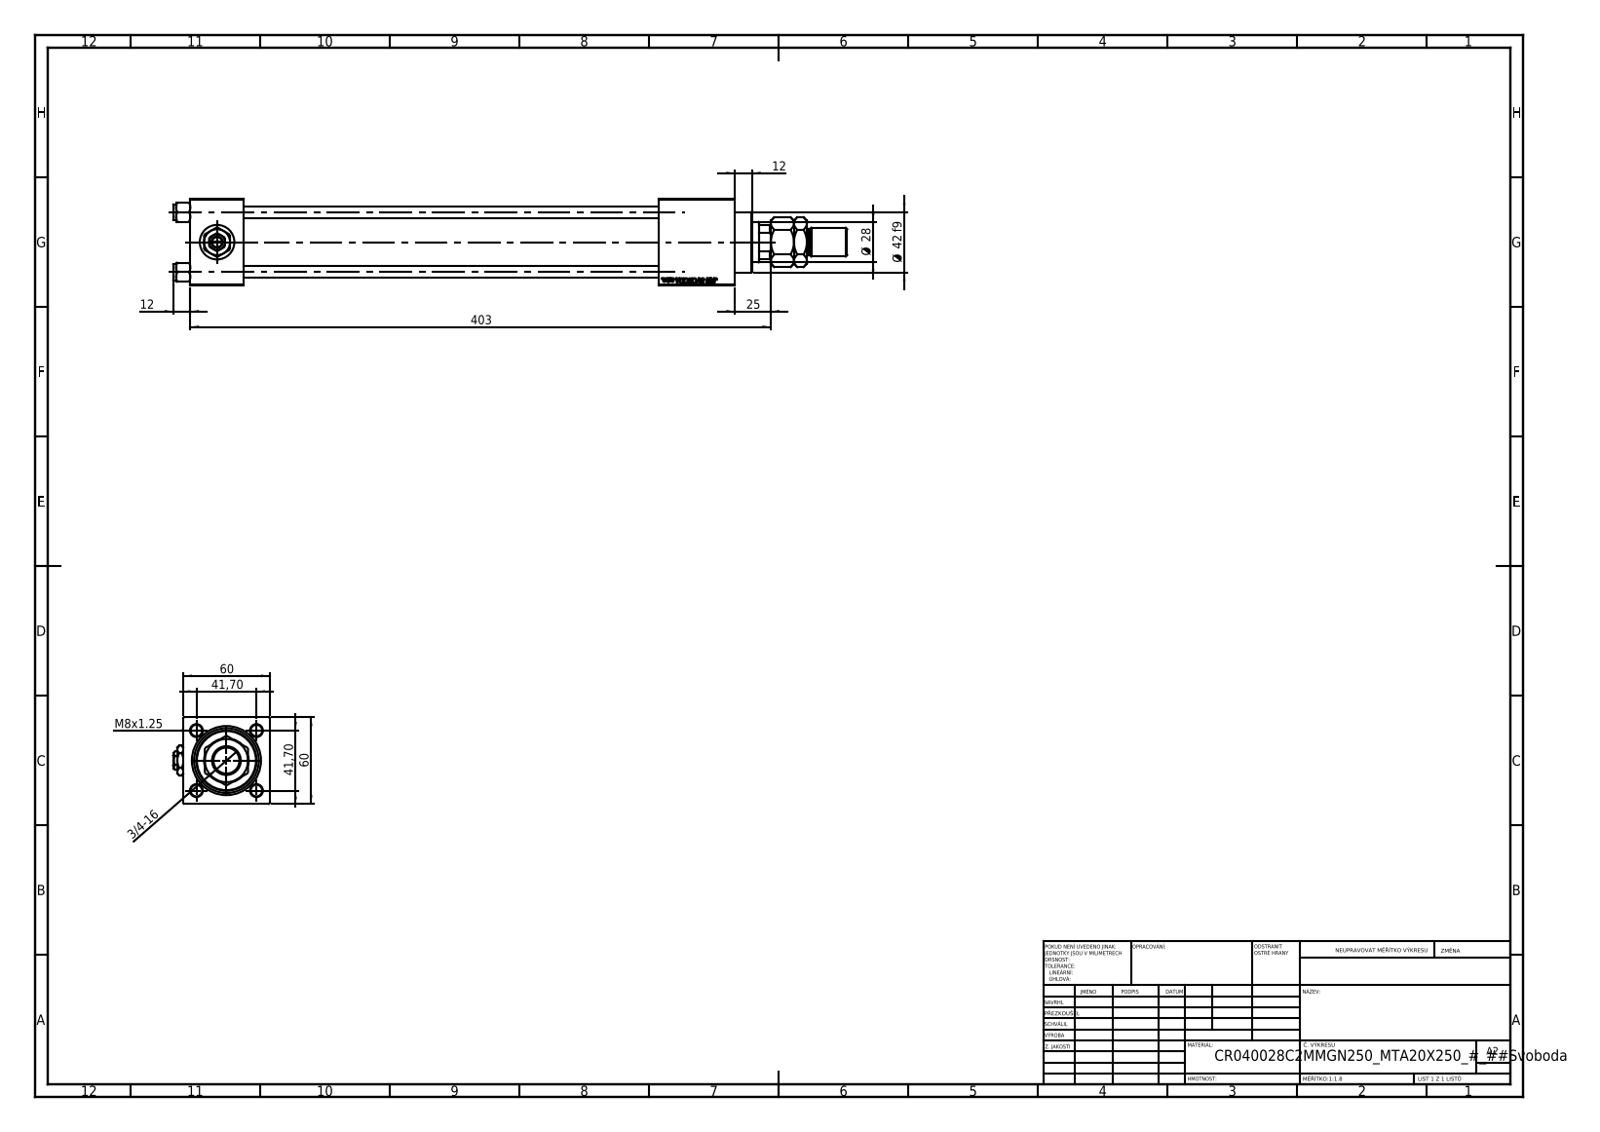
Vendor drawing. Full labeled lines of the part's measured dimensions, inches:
Part name (STEP PRODUCT): MTA; V215CR_VCP_C; NUT_M5_C; V215CR_C_Body (+3 more)
STEP written by: SolidWorks 2019 (CONFIG_CONTROL_DESIGN)
Units: inches
Bodies: 13 solids, 1251 faces (565 planar, 98 cylindrical, 588 other)
Overall size (bounding box): 18.425 × 2.638 × 2.362
Volume: 44.66 in³ · Surface area: 347.9 in²
Round holes (diameter × count): ⌀0.315 ×4, ⌀0.276 ×2, ⌀0.656 ×2, ⌀0.945 ×2, ⌀0.728 ×1, ⌀1.102 ×1, ⌀1.22 ×1, ⌀1.575 ×1, ⌀1.772 ×1
Round bosses / shafts (diameter × count): ⌀0.433 ×4, ⌀1.811 ×1, ⌀1.654 ×1, ⌀0.787 ×1, ⌀0.709 ×1
Partial cylindrical surfaces — rounded edges, fillets, slot ends (radius × count): R0.531 ×1
Main face-to-face distances: 2.362, 1.457, 12.795, 11.339, 2.087, 13.752, 12.295, 0.957, 14.882, 13.425
Hole centre spacings: 1.161, 1.642, 2.322, 12.697
